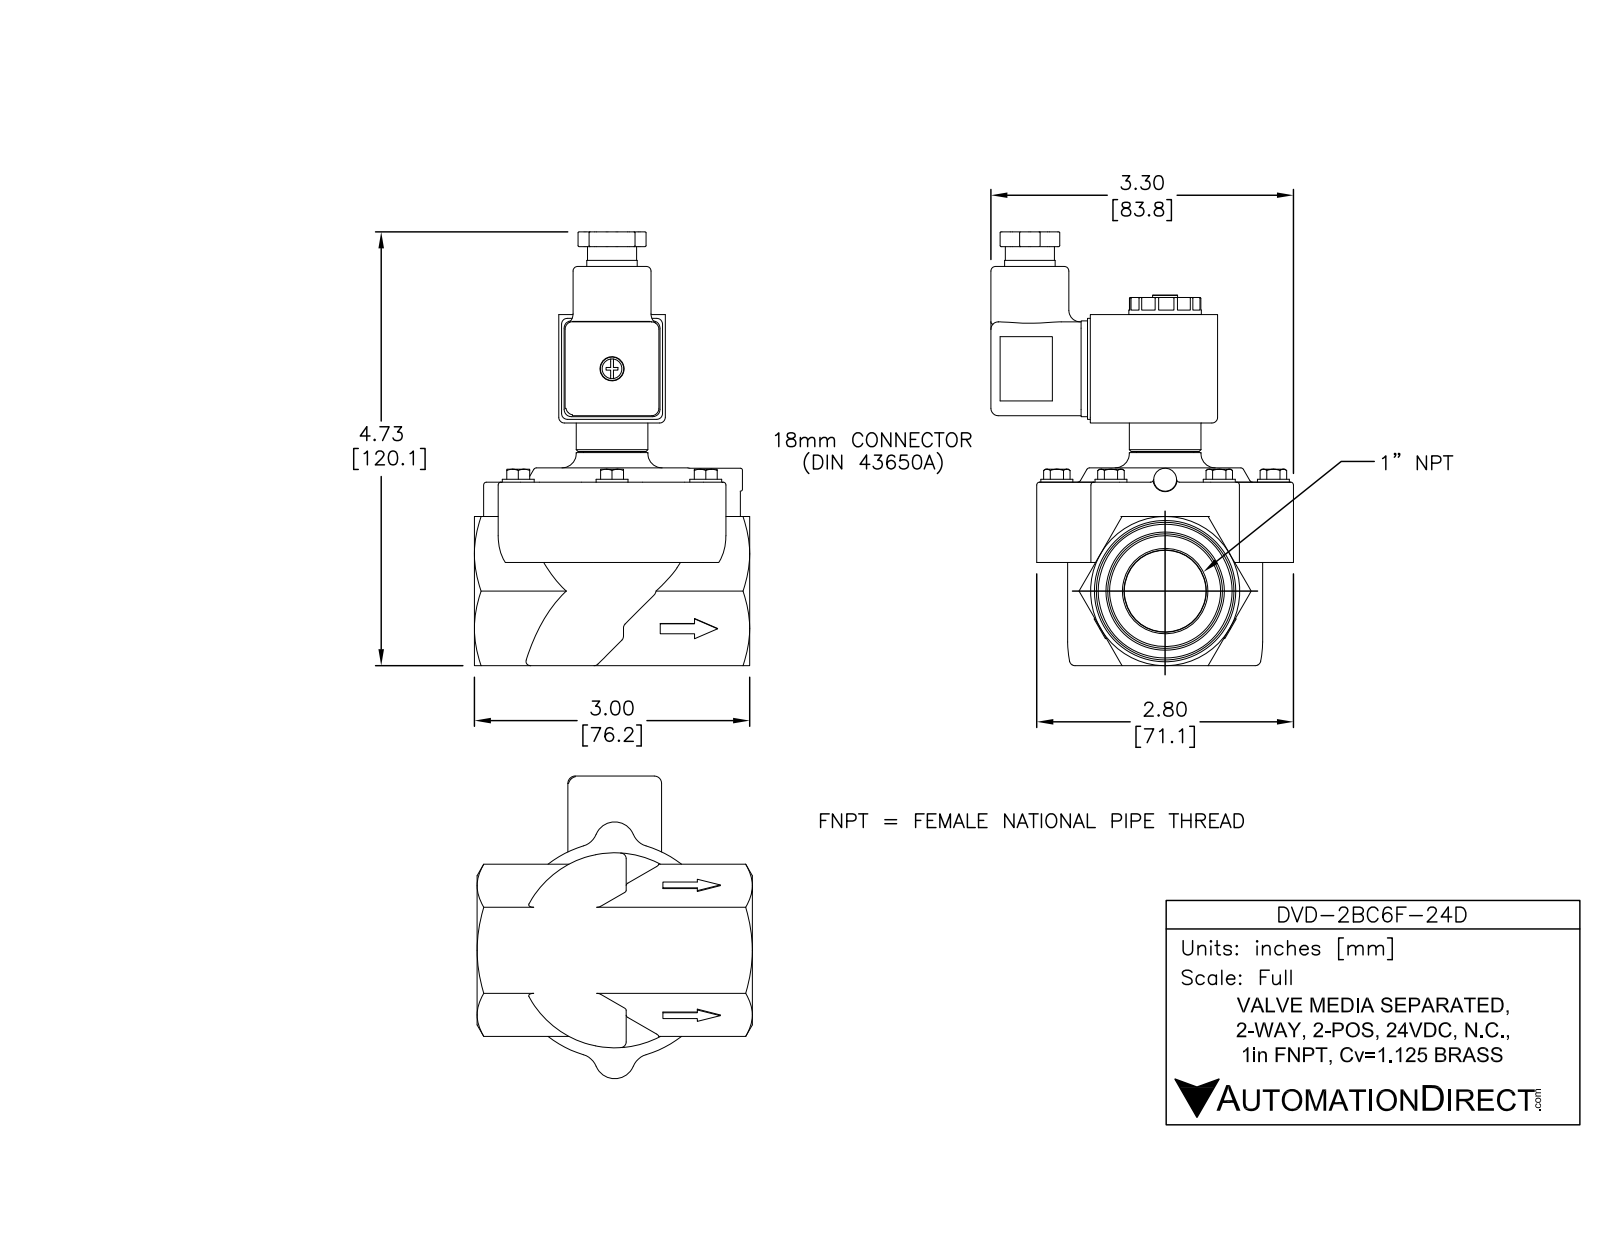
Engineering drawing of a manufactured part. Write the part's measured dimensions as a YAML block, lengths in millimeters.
part_name: "DVD-2BC6F-24D"
step_written_by: "SolidWorks 2015 (AUTOMOTIVE_DESIGN)"
units: millimeters
bodies: {solids: 2, faces: 1898, planar: 894, cylindrical: 390, other: 614}
overall_size: [120.1, 83.8, 76.2]
volume: 135800
surface_area: 65420
round_holes:
  - {diameter: 5.1, count: 6}
  - {diameter: 6, count: 6}
  - {diameter: 4.7, count: 4}
  - {diameter: 1.5, count: 2}
  - {diameter: 3.2, count: 2}
  - {diameter: 4, count: 2}
  - {diameter: 4.7, count: 2}
  - {diameter: 28.6, count: 2}
  - {diameter: 1.2, count: 1}
  - {diameter: 1.7, count: 1}
  - {diameter: 1.7, count: 1}
  - {diameter: 2, count: 1}
round_bosses_or_shafts:
  - {diameter: 8.8, count: 6}
  - {diameter: 5.9, count: 6}
  - {diameter: 4.2, count: 6}
  - {diameter: 46.8, count: 1}
  - {diameter: 38.1, count: 1}
  - {diameter: 34.5, count: 1}
  - {diameter: 21.6, count: 1}
  - {diameter: 20.1, count: 1}
partial_cylinders:
  - {radius: 0.3, count: 48}
  - {radius: 5.6, count: 20}
  - {radius: 4, count: 16}
  - {radius: 1.6, count: 12}
  - {radius: 2, count: 12}
  - {radius: 0.8, count: 10}
  - {radius: 1.3, count: 8}
  - {radius: 0.8, count: 7}
face_to_face_distances: [40.9, 3.2, 41.4, 0.5, 41.3, 3.9, 1.2, 3, 26.5, 24.7]
hole_center_spacings: [30, 30, 51.9, 15.5, 42.4, 57.9, 28, 29.7]
